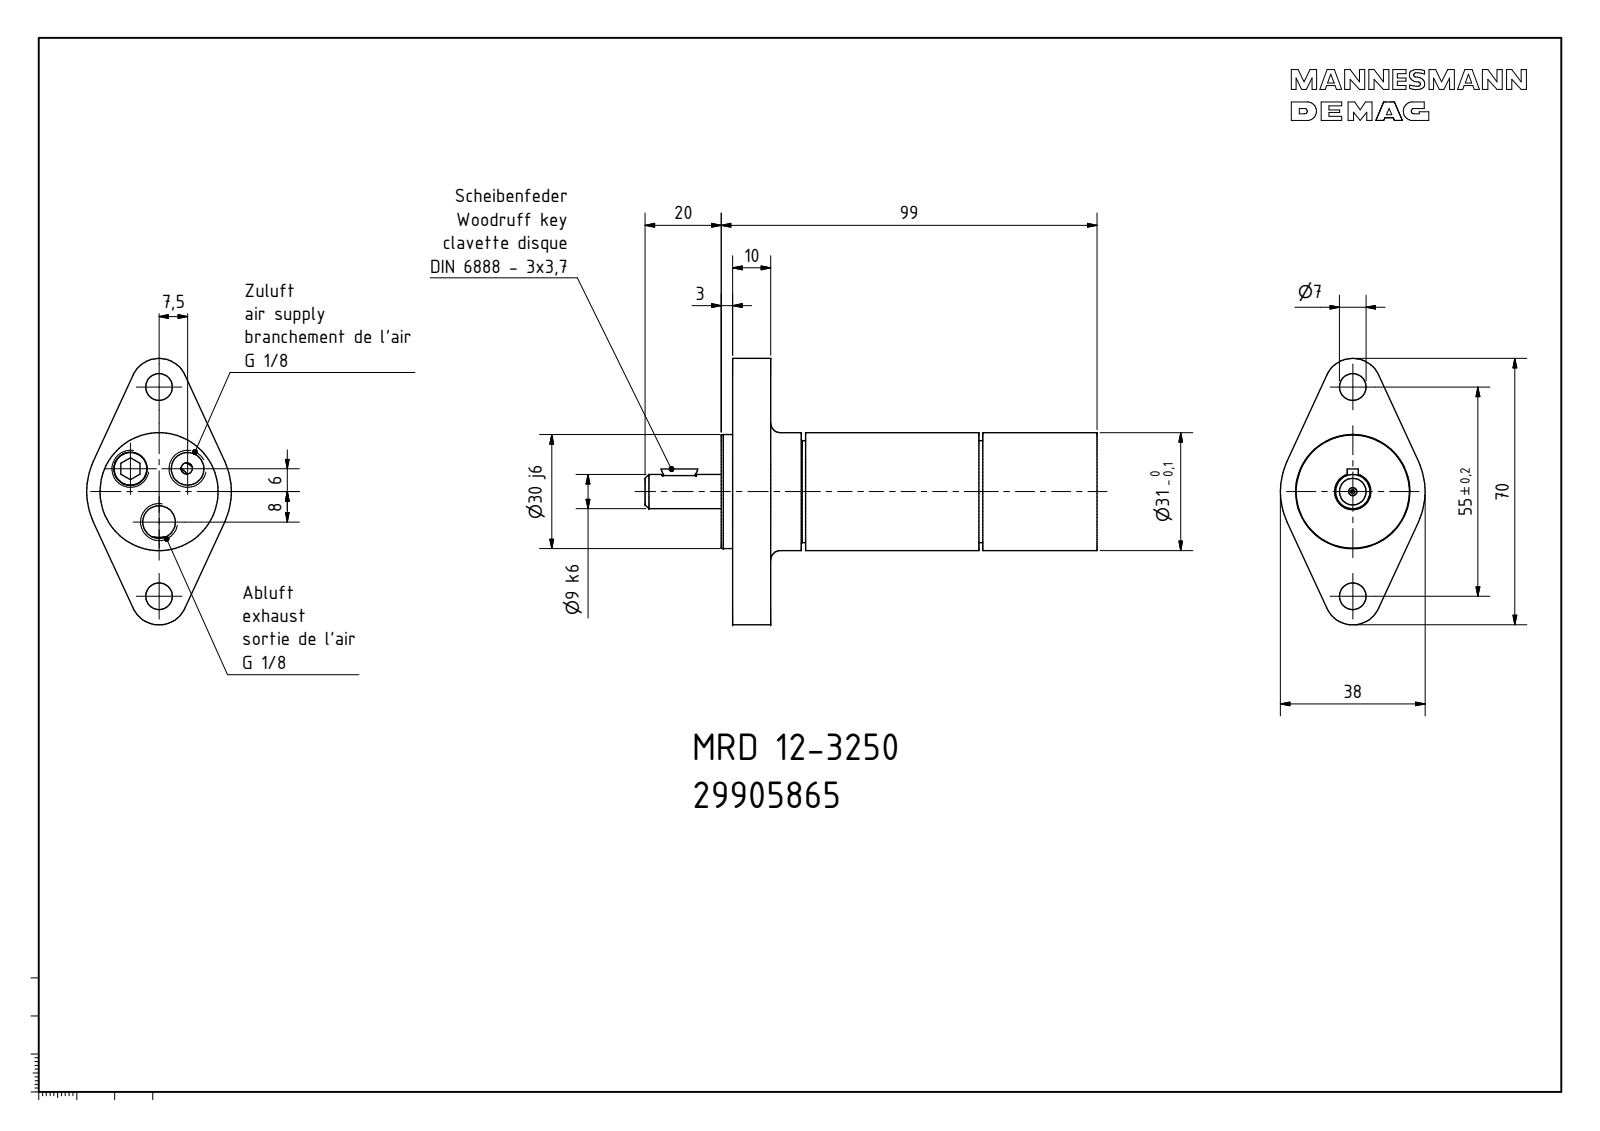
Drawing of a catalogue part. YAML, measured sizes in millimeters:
part_name: "MRD 12-3250_29905865"
step_written_by: "Autodesk Inventor 2008 (CONFIG_CONTROL_DESIGN)"
units: millimeters
bodies: {solids: 1, faces: 59, planar: 33, cylindrical: 13, other: 13}
overall_size: [118.7, 70, 38]
volume: 83178
surface_area: 15941
round_bosses_or_shafts:
  - {diameter: 31, count: 1}
  - {diameter: 30, count: 1}
  - {diameter: 29.79, count: 1}
  - {diameter: 9, count: 1}
partial_cylinders:
  - {radius: 7.5, count: 2}
  - {radius: 5, count: 1}
  - {radius: 5.25, count: 1}
  - {radius: 19, count: 1}
face_to_face_distances: [10, 3, 13, 98.7, 95.7, 85.7, 37.98, 86.24, 83.24, 73.24]
